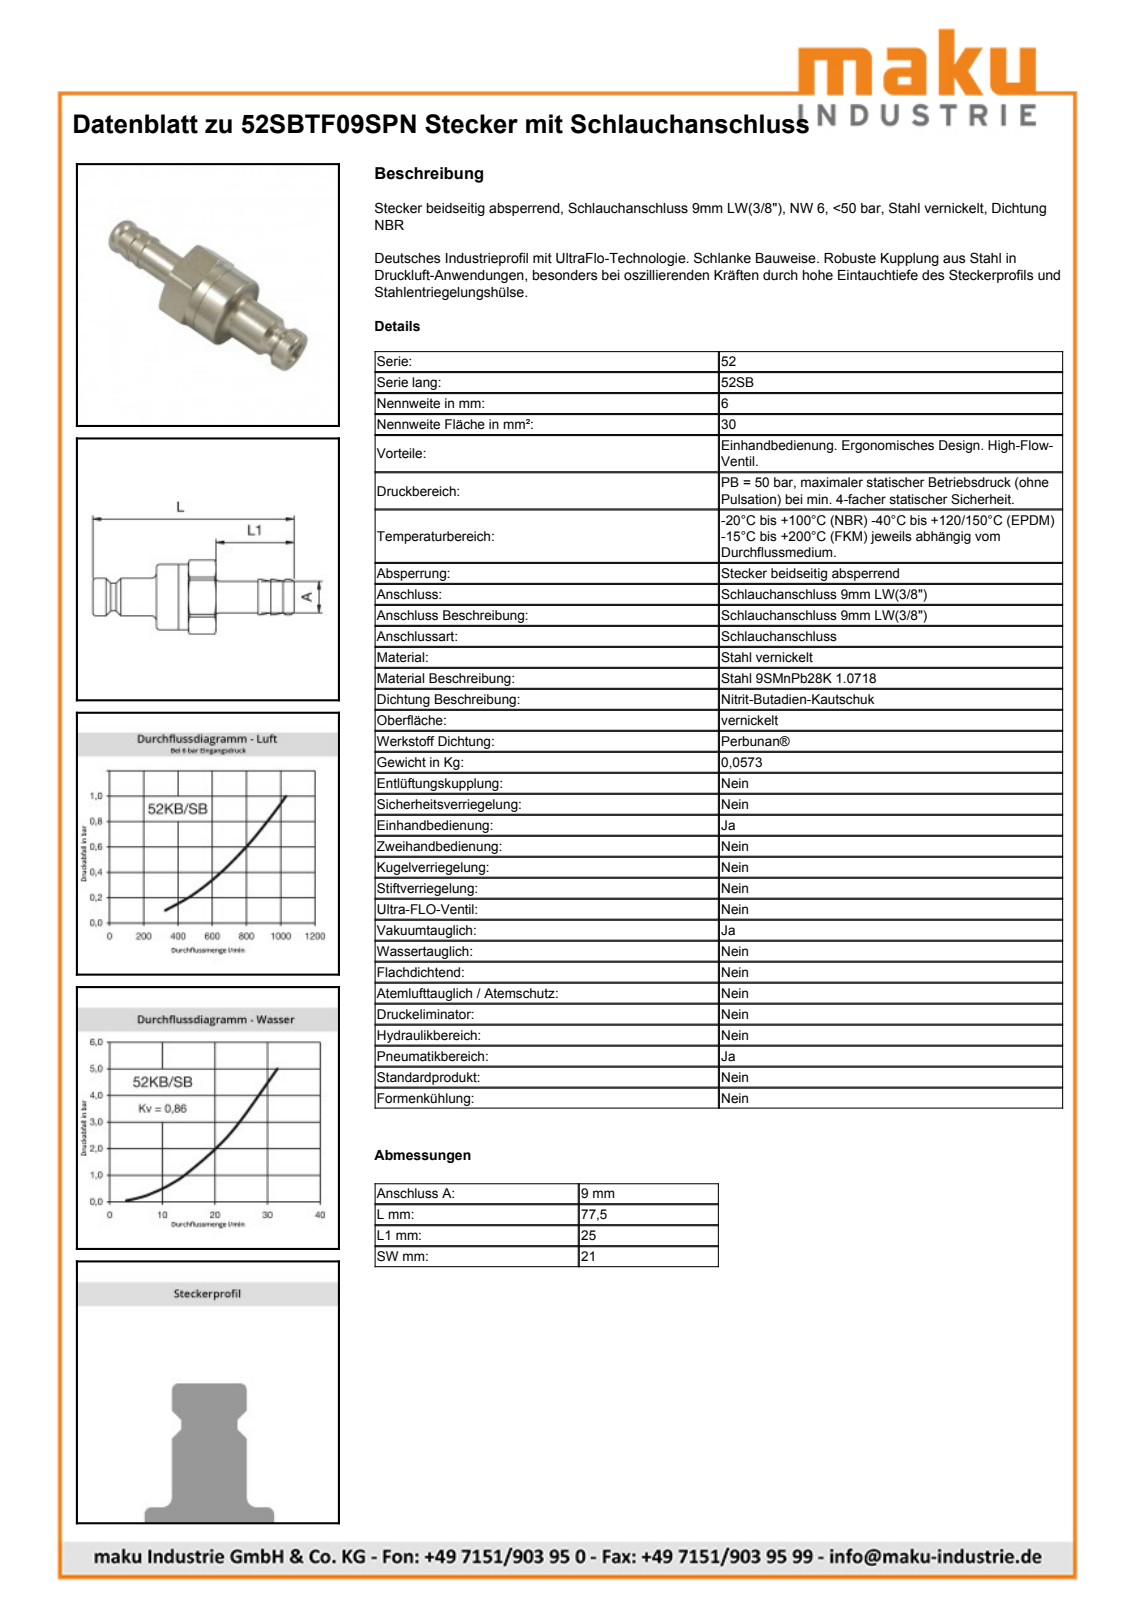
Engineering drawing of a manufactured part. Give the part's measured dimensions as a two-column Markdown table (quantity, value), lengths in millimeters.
| quantity | value |
| --- | --- |
| part name | D111715 |
| STEP written by | Autodesk Inventor 2013 (AUTOMOTIVE_DESIGN) |
| units | millimeters |
| bodies | 1 solid, 50 faces (13 planar, 12 cylindrical, 25 other) |
| overall size | 64.5 × 23.7 × 21.49 |
| volume | 10 804 mm³ |
| surface area | 3 579 mm² |
| round bosses / shafts (diameter × count) | 21 × 1, 17.46 × 1, 11.95 × 1, 9.1 × 1, 8.9 × 1 |
| partial cylindrical surfaces (radius × count) | 11.85 × 1 |
| main face-to-face distances | 21, 19.1, 20.4, 39.5, 64.5, 44.1, 25, 27.5, 7.1, 12 |
